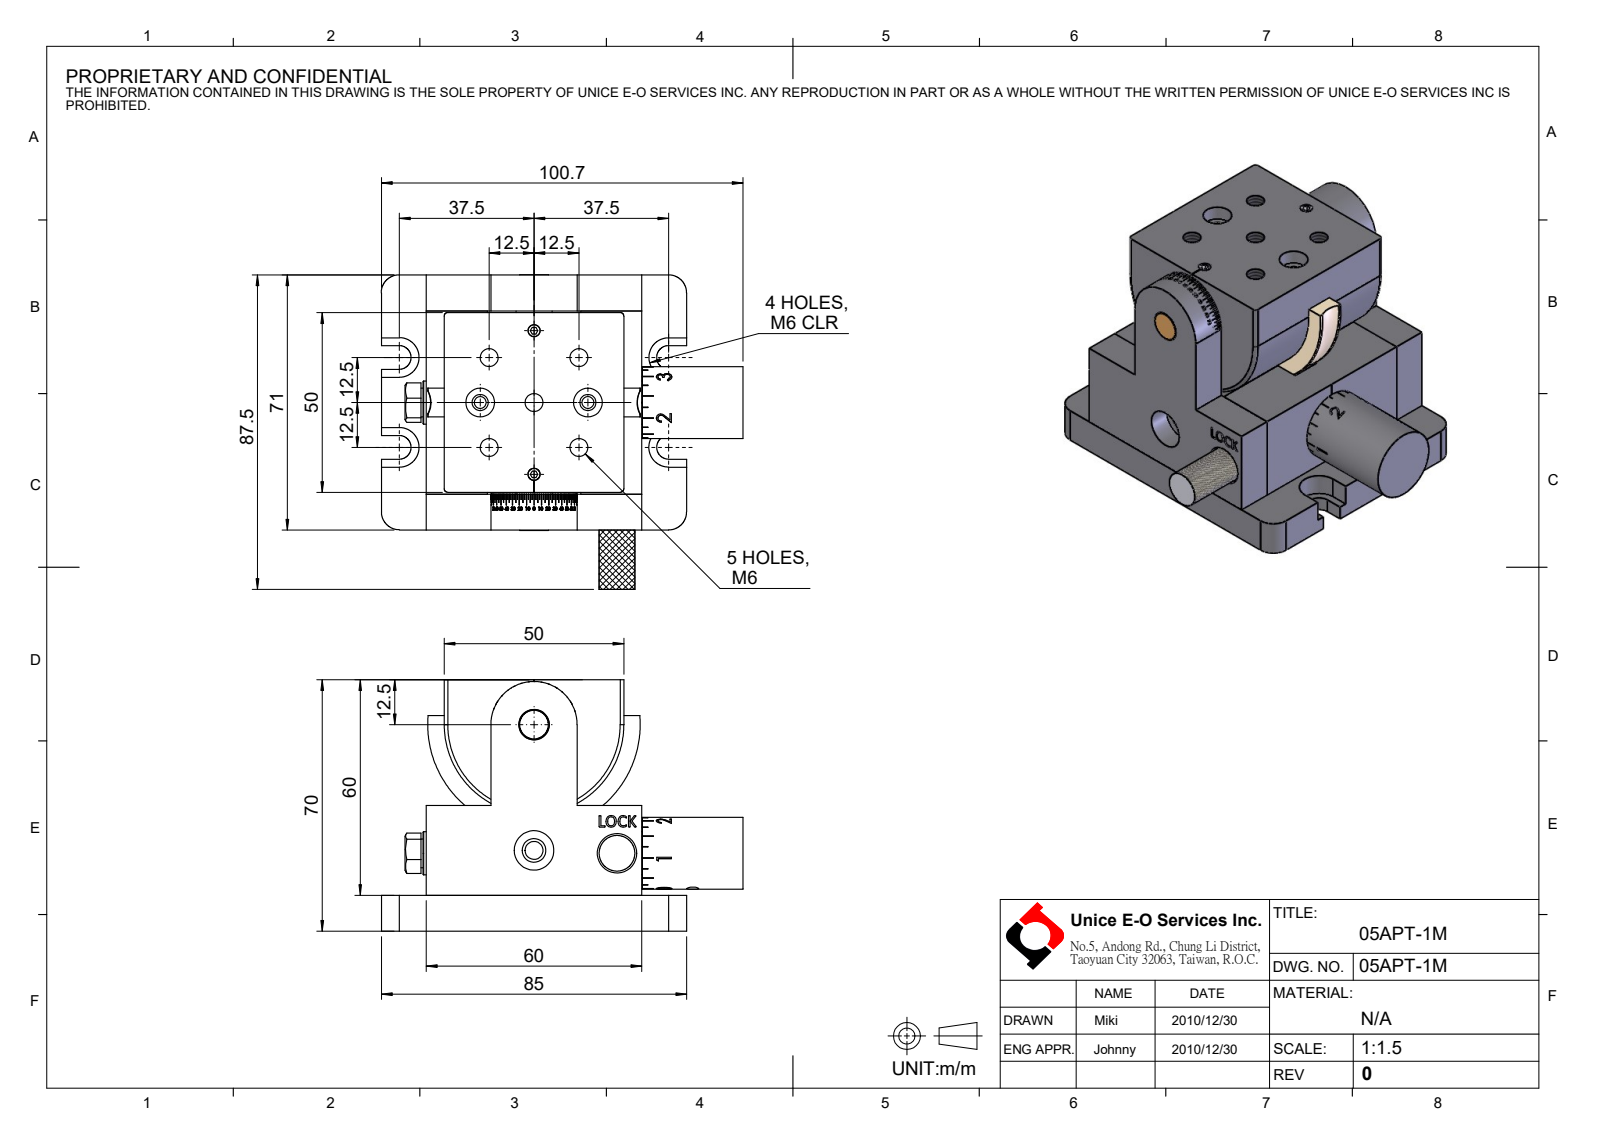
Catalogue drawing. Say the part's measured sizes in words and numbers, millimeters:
The part is named "05APT-1M". Its 3-D file was written by "SolidWorks 2016 (CONFIG_CONTROL_DESIGN)". It is 21 solids with 2321 faces: 1047 planar, 310 cylindrical and 964 other. Overall it measures 100.7 by 87.6 by 70 millimeters. Its volume is 253 078 cubic millimeters and its surface area 78 275 square millimeters. Round holes: 13 of diameter 5, 8 of diameter 11, 5 of diameter 3.3, 5 of diameter 6.6, 3 of diameter 8, 2 of diameter 4.5, 2 of diameter 10, 2 of diameter 12, 1 of diameter 4.2, 1 of diameter 6, 1 of diameter 6.65, 1 of diameter 8.5. Round bosses or shafts: 3 of diameter 4, 2 of diameter 9, 1 of diameter 20, 1 of diameter 15.6, 1 of diameter 10, 1 of diameter 8, 1 of diameter 7.5, 1 of diameter 5. Partial cylindrical surfaces (rounded edges, fillets, slot ends): 4 of radius 1, 4 of radius 3.3, 4 of radius 3.5, 4 of radius 5, 4 of radius 5.5, 1 of radius 7.34, 1 of radius 9.98, 1 of radius 11.98. The main face-to-face distances are 10, 61, 31.5, 39.5, 21.5, 29.5, 60, 35, 51, 10.5. The hole center spacings are 25, 33.35, 20, 40, 10.61, 12.75, 14.58, 15.
